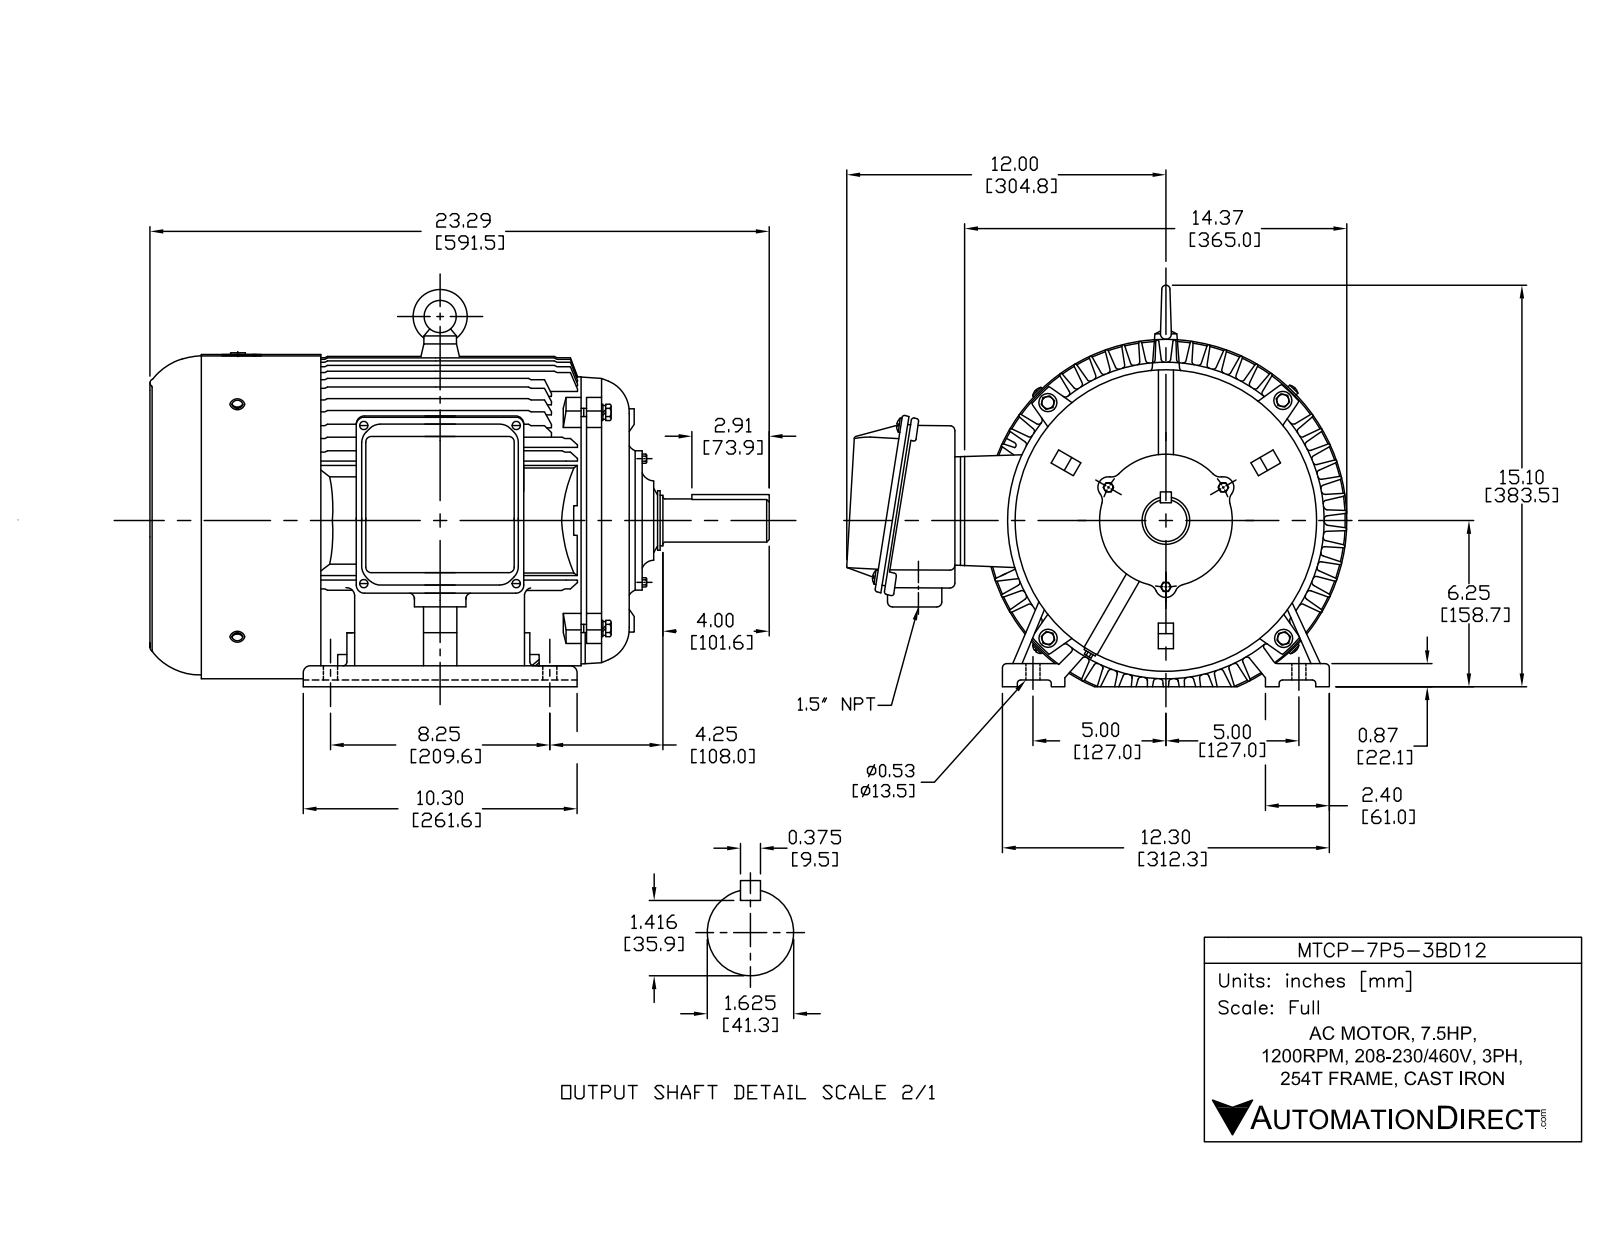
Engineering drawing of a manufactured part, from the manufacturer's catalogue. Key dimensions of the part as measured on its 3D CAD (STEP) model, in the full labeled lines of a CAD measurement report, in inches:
Part name (STEP PRODUCT): 17橡皮塞; PE250-280接线盒座_默认_按加工; hex head bolts-full thread grade c gb_GB_FASTENER_BOLT_HHBFTC M10X45-N; eyebolts gb_GB_FASTENER_SCREWS_FRS M12-N (+8 more)
STEP written by: SolidWorks 2017 (AUTOMOTIVE_DESIGN)
Units: inches
Bodies: 67 solids, 3916 faces (991 planar, 1400 cylindrical, 1525 other)
Overall size (bounding box): 23.579 × 18.501 × 15.663
Volume: 502.6 in³ · Surface area: 3 641 in²
Round holes (diameter × count): ⌀0.276 ×14, ⌀0.197 ×12, ⌀0.315 ×8, ⌀0.335 ×6, ⌀0.669 ×5, ⌀0.252 ×4, ⌀0.263 ×4, ⌀0.354 ×4, ⌀0.413 ×4, ⌀0.429 ×4, ⌀0.433 ×4, ⌀0.448 ×4
Round bosses / shafts (diameter × count): ⌀0.236 ×11, ⌀0.472 ×5, ⌀0.394 ×5, ⌀0.787 ×4, ⌀0.634 ×4, ⌀0.389 ×4, ⌀0.197 ×2, ⌀13.976 ×1
Partial cylindrical surfaces — rounded edges, fillets, slot ends (radius × count): R0.039 ×255, R0.02 ×92, R0.118 ×72, R0.197 ×68, R0.059 ×36, R0.157 ×32, R0.315 ×26, R0.394 ×20
Main face-to-face distances: 0.197, 0.059, 0.315, 18.181, 18.122, 0.669, 0.394, 18.496, 18.437, 3.069
Hole centre spacings: 2.953, 2.264, 2.952, 4.176, 5.669, 4.232, 5.038, 5.34
